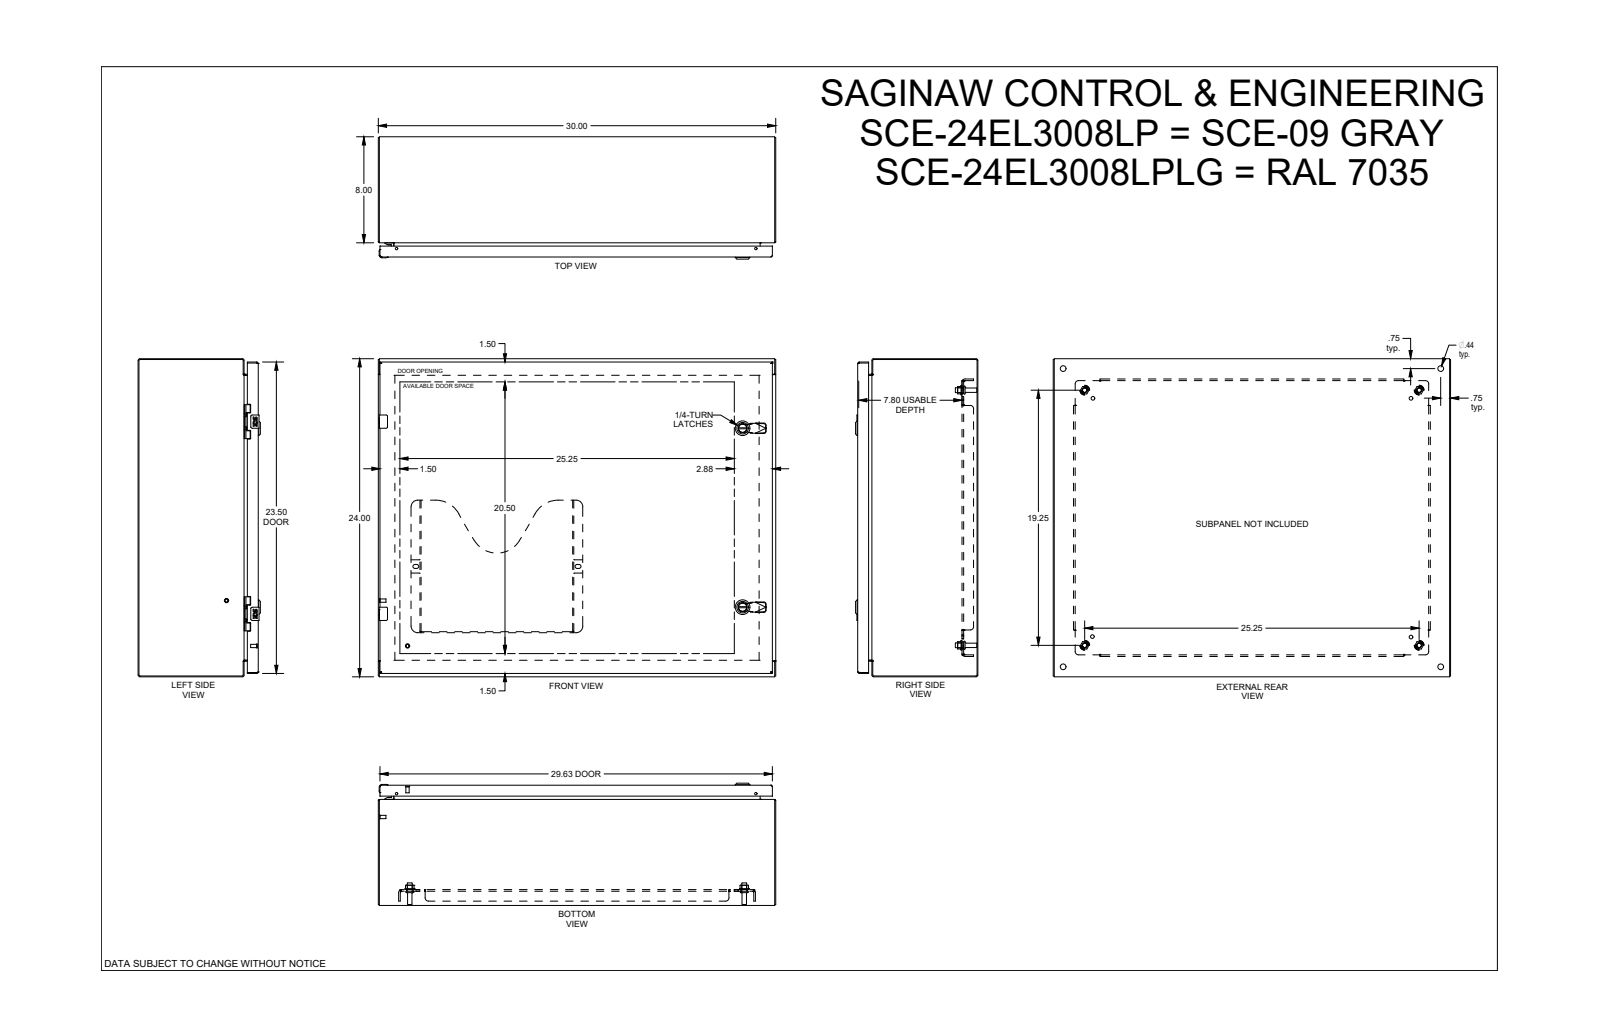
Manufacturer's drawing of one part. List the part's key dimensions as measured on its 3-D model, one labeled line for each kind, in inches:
Part name (STEP PRODUCT): SCE-24EL3008LP
STEP written by: SolidWorks 2021 (AUTOMOTIVE_DESIGN)
Units: inches
Bodies: 47 solids, 2843 faces (1115 planar, 858 cylindrical, 870 other)
Overall size (bounding box): 30 × 24 × 9.23
Volume: 287.1 in³ · Surface area: 6 888 in²
Round holes (diameter × count): ⌀0.172 ×4, ⌀0.205 ×4, ⌀0.244 ×4, ⌀0.266 ×4, ⌀0.281 ×4, ⌀0.367 ×4, ⌀0.375 ×4, ⌀0.437 ×4, ⌀0.5 ×4, ⌀0.04 ×2, ⌀0.188 ×2, ⌀0.197 ×2
Round bosses / shafts (diameter × count): ⌀0.17 ×6, ⌀0.366 ×4, ⌀0.332 ×4, ⌀0.25 ×4, ⌀0.248 ×4, ⌀0.24 ×4, ⌀0.196 ×3, ⌀1.102 ×2
Partial cylindrical surfaces — rounded edges, fillets, slot ends (radius × count): R0.012 ×56, R0.01 ×28, R0.015 ×24, R0.02 ×20, R0.04 ×17, R0.06 ×13, R0.029 ×12, R0.1 ×12
Main face-to-face distances: 0.075, 0.06, 8.998, 9.073, 9.013, 8.938, 1.2, 7.873, 1.125, 0.125
Hole centre spacings: 14.5, 0.02, 0.493, 0.985, 0.875, 3.173, 4.493, 20.38
